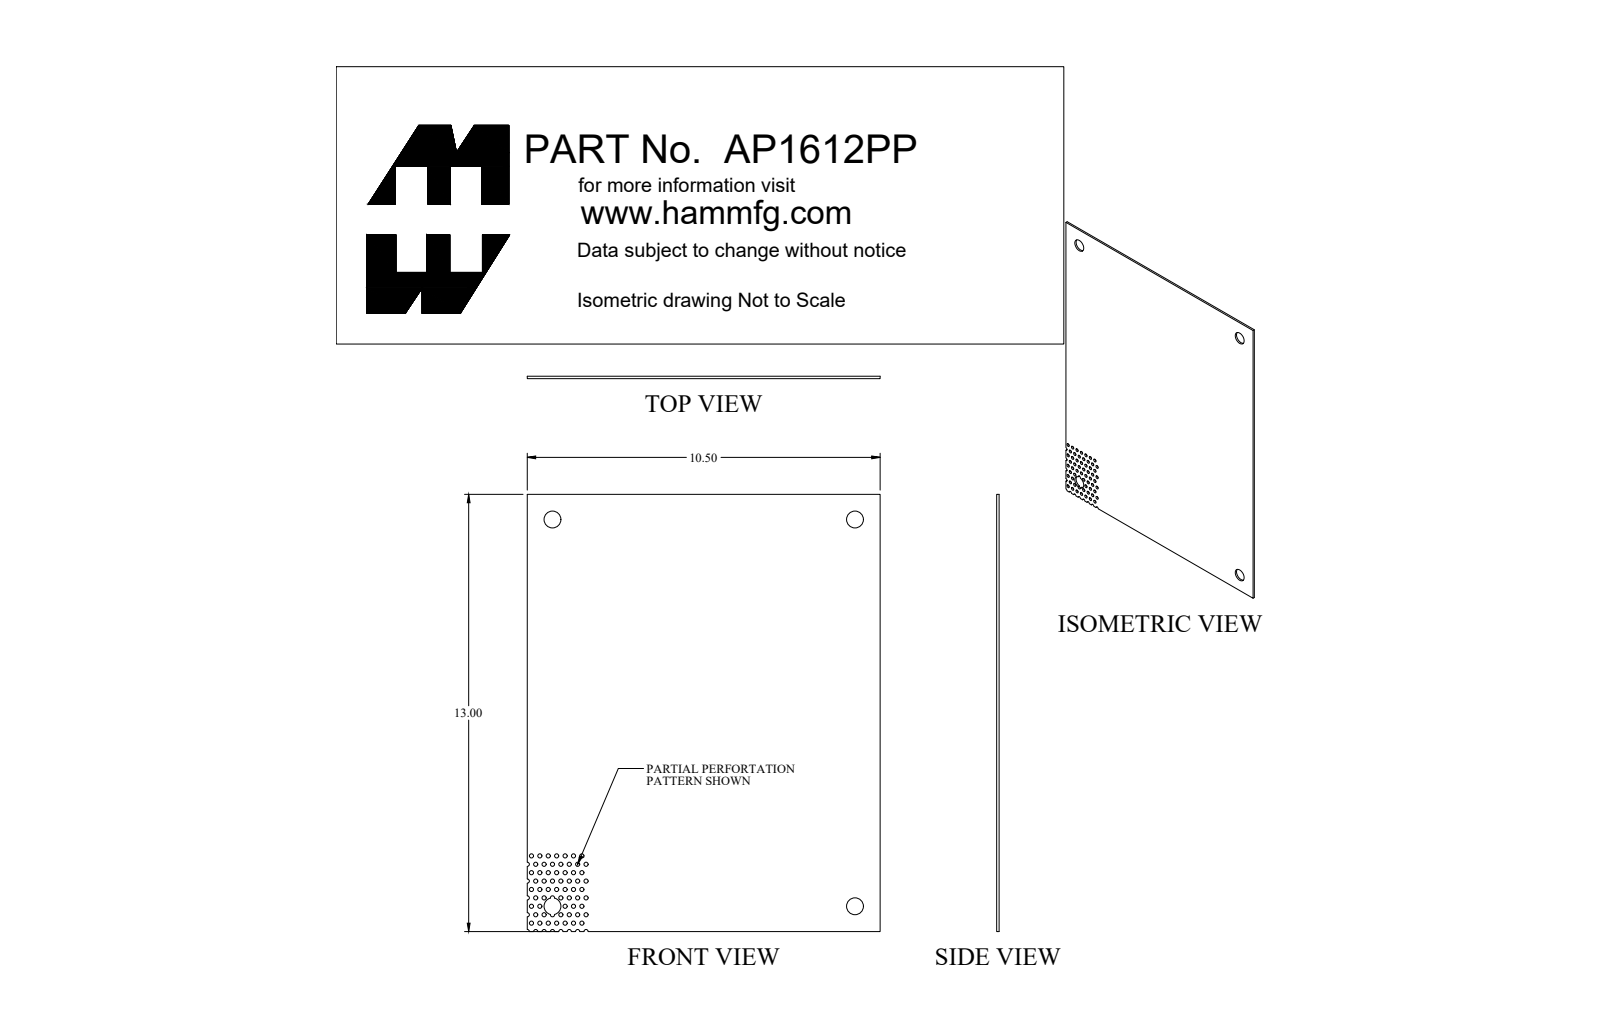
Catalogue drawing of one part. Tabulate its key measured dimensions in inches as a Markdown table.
| quantity | value |
| --- | --- |
| part name | AP1612PP_Default |
| STEP written by | SolidWorks 2019 (CONFIG_CONTROL_DESIGN) |
| units | inches |
| bodies | 1 solid, 165 faces (17 planar, 148 cylindrical, 0 other) |
| overall size | 13 × 10.5 × 0.072 |
| volume | 9.713 in³ |
| surface area | 275.4 in² |
| round holes (diameter × count) | 0.125 × 38, 0.125 × 21, 0.5 × 4 |
| partial cylindrical surfaces (radius × count) | 0.062 × 13, 0.063 × 1 |
| main face-to-face distances | 0.072, 10.5, 13 |
| hole center spacings | 0.28, 0.5, 0.25, 0.559, 1.152, 1.118, 0.76, 0.707 |
